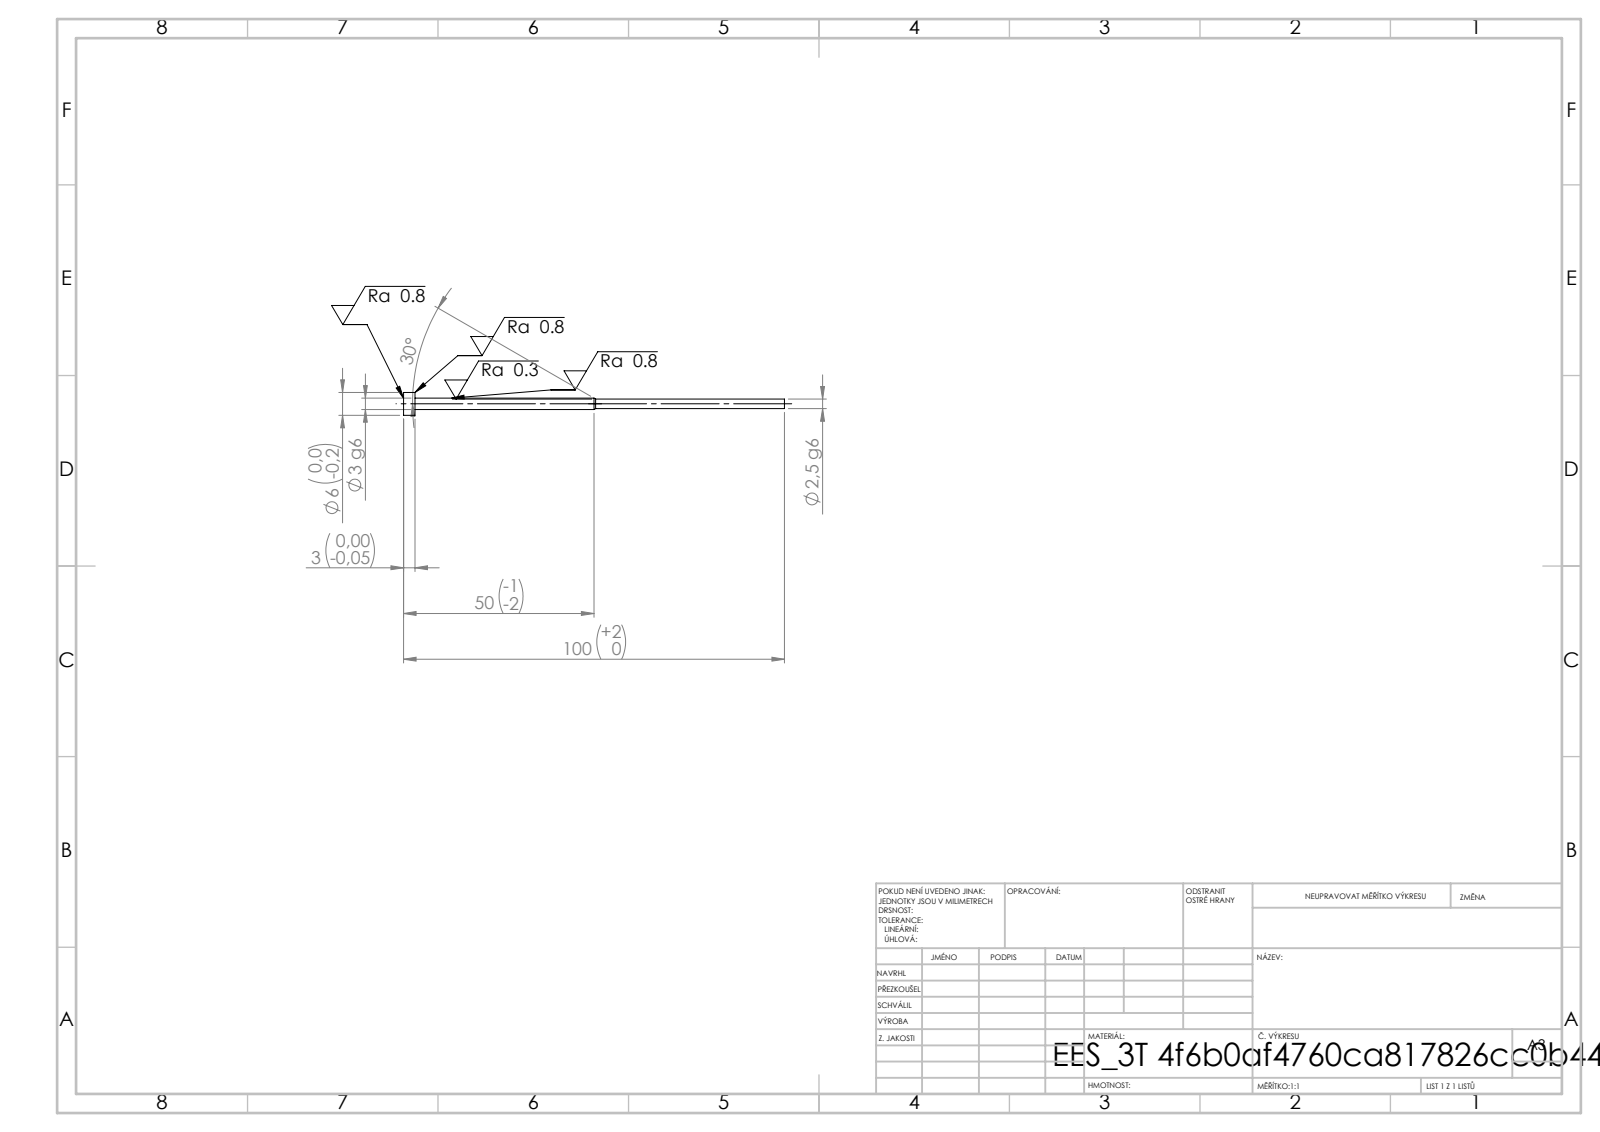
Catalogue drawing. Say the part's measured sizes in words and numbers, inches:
Its 3-D file was written by "SolidWorks 2019 (CONFIG_CONTROL_DESIGN)". It is 1 solid with 11 faces: 3 planar, 6 cylindrical and 2 other. Overall it measures 3.937 by 0.236 by 0.236 inches. Its volume is 0.04 cubic inches and its surface area 1.47 square inches. Round bosses or shafts: 1 of diameter 0.236, 1 of diameter 0.118, 1 of diameter 0.098. The main face-to-face distances are 0.118, 3.819, 3.937.
